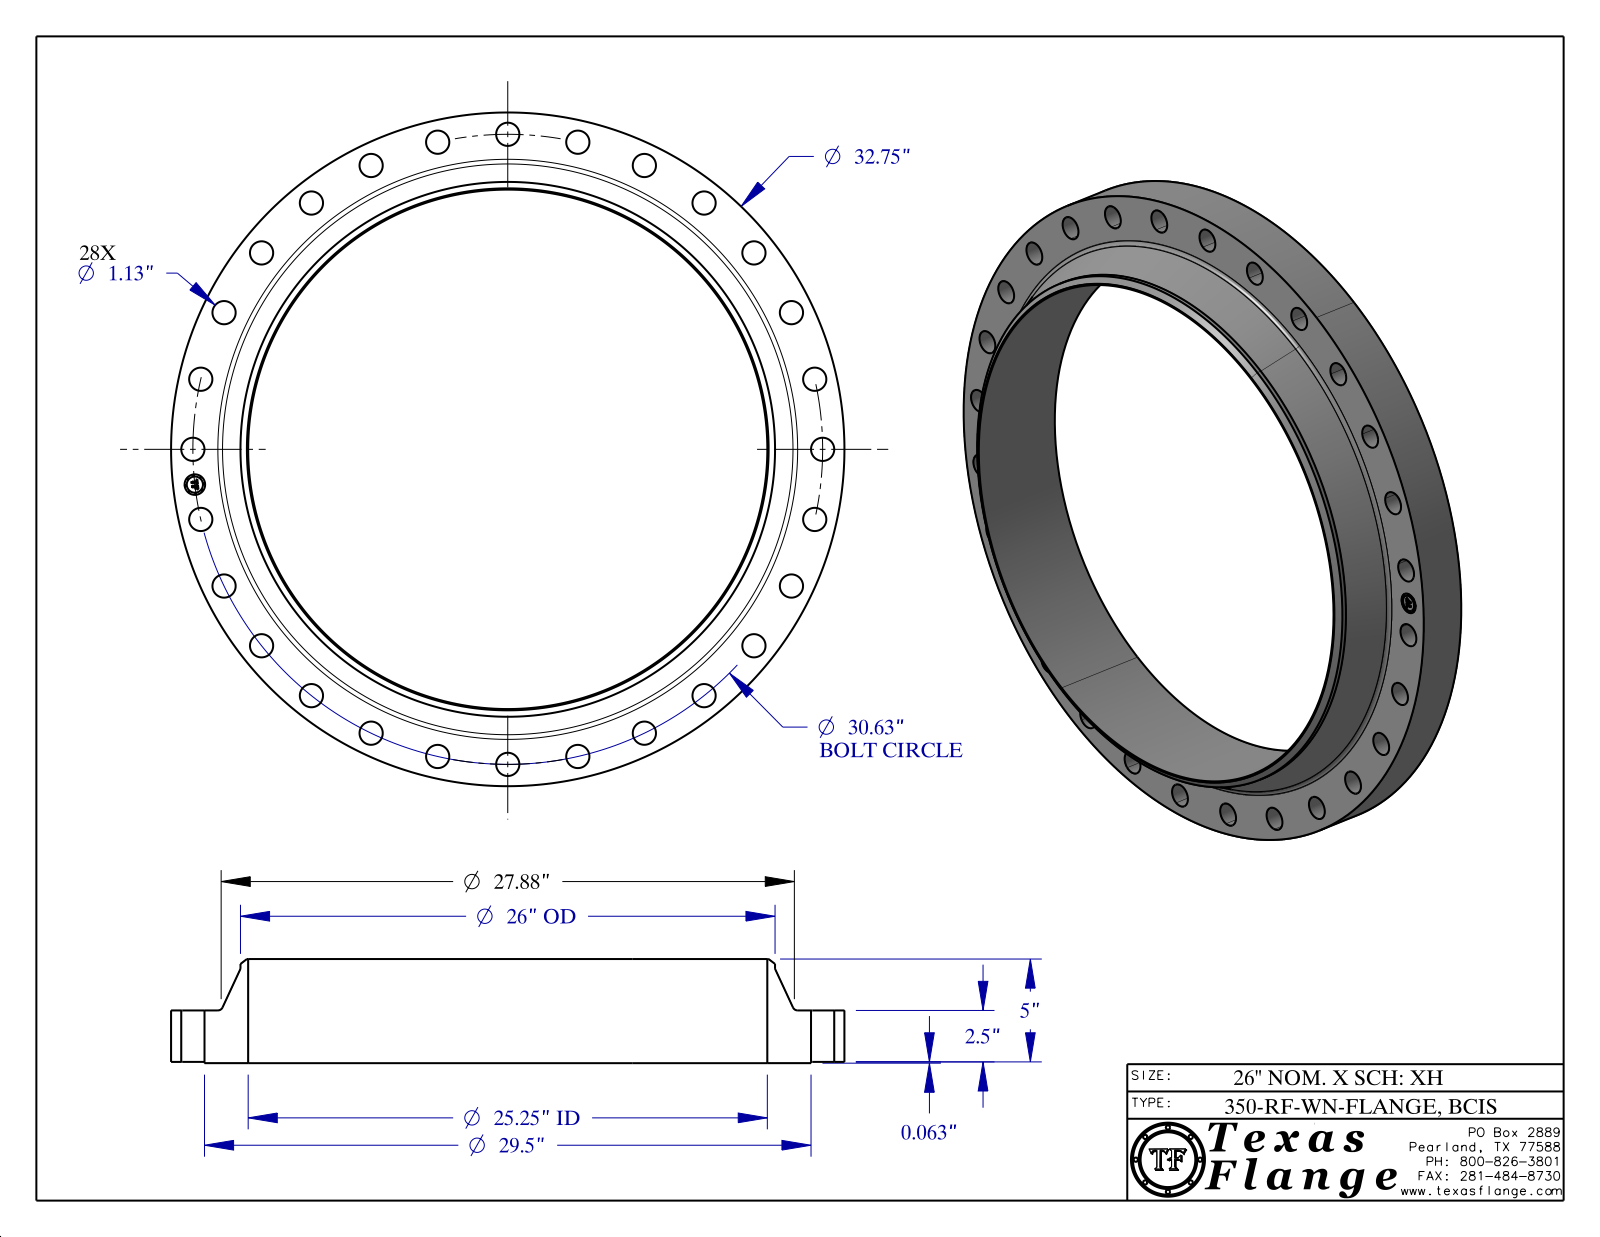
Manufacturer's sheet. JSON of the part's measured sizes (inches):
{"part_name": "350-RF-WN, BCIS", "step_written_by": "CATIA V5 STEP AP214 (AUTOMOTIVE_DESIGN)", "units": "inches", "bodies": {"solids": 1, "faces": 459, "planar": 369, "cylindrical": 84, "other": 6}, "overall_size": [32.75, 32.75, 5.063], "volume_in3": 947.7, "surface_area_in2": 1673, "round_holes": [[1.13, 28], [1, 1], [25.25, 1]], "round_bosses_or_shafts": [[0.061, 8], [32.75, 1], [29.5, 1], [26, 1], [0.788, 1]], "face_to_face_distances": [2.563, 2.5, 0.063, 5.063, 5, 0.015, 2.548, 2.485, 2.515, 0.298], "hole_center_spacings": [10.117, 15.315, 21.659, 29.862, 30.437, 3.43, 16.296, 23.948]}
